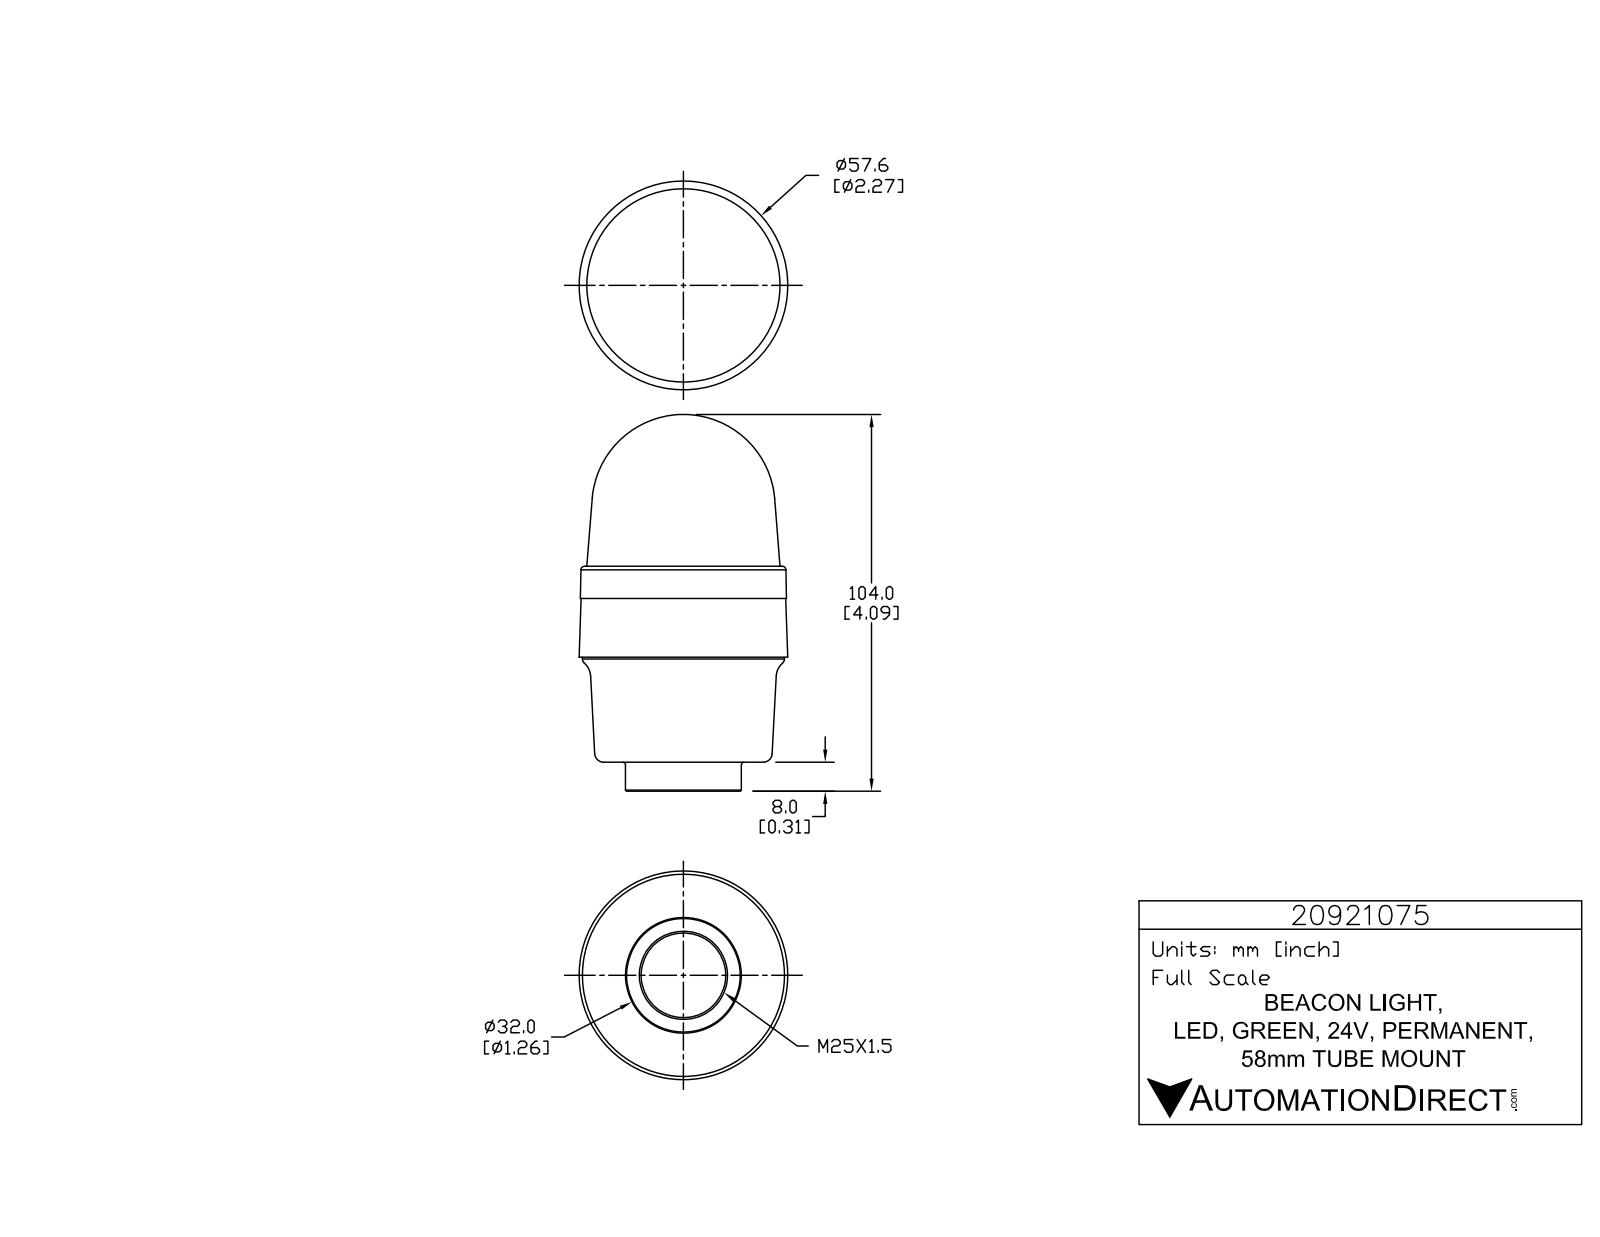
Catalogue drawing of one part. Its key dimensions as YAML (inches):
part_name: "20921075"
step_written_by: "SolidWorks 2015 (AUTOMOTIVE_DESIGN)"
units: inches
bodies: {solids: 1, faces: 791, planar: 525, cylindrical: 168, other: 98}
overall_size: [4.051, 2.269, 2.269]
volume: 11.72
surface_area: 29.93
round_holes:
  - {diameter: 0.039, count: 3}
  - {diameter: 0.92, count: 1}
round_bosses_or_shafts:
  - {diameter: 0.226, count: 3}
  - {diameter: 0.056, count: 3}
  - {diameter: 2.197, count: 1}
  - {diameter: 1.26, count: 1}
partial_cylinders:
  - {radius: 0.008, count: 6}
  - {radius: 0.008, count: 6}
  - {radius: 0.008, count: 6}
  - {radius: 0.131, count: 6}
  - {radius: 0.004, count: 3}
  - {radius: 0.005, count: 3}
  - {radius: 0.008, count: 3}
  - {radius: 0.008, count: 3}
face_to_face_distances: [0.315, 1.142, 1.457, 0.988, 2.13, 2.445, 0.35, 0.638, 1.78, 2.094]
